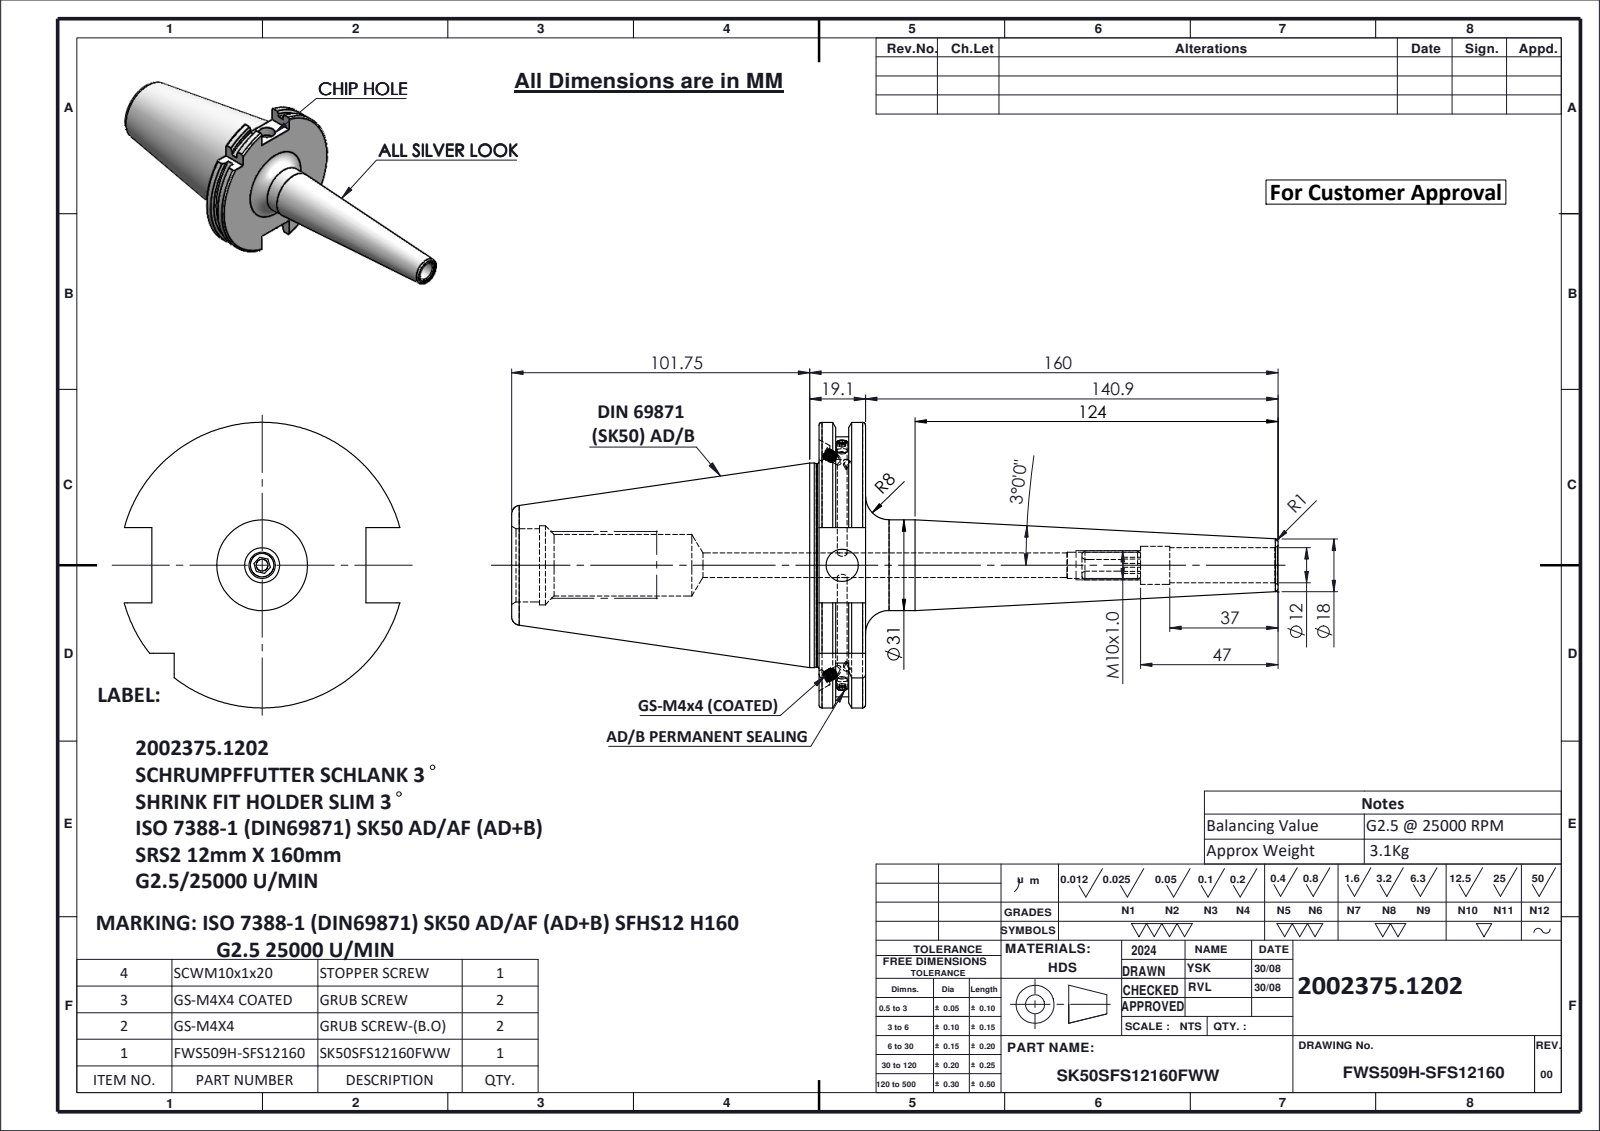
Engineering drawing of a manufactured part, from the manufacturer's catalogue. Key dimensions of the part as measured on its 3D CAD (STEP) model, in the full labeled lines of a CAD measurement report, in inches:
Part name (STEP PRODUCT): SK50SFS12160FWW; FWS509H-SFS12160; GS-M4X4_DIN 913 - M4 x 4-N; SCWM10X1 (+1 more)
STEP written by: SolidWorks 2024 (CONFIG_CONTROL_DESIGN)
Units: inches
Bodies: 6 solids, 275 faces (72 planar, 81 cylindrical, 122 other)
Overall size (bounding box): 10.305 × 3.839 × 3.703
Volume: 24.36 in³ · Surface area: 91.68 in²
Round holes (diameter × count): ⌀0.126 ×2, ⌀0.236 ×2, ⌀0.13 ×1, ⌀0.157 ×1, ⌀0.331 ×1, ⌀0.354 ×1, ⌀0.433 ×1, ⌀0.472 ×1, ⌀0.512 ×1, ⌀0.827 ×1, ⌀0.984 ×1, ⌀1.063 ×1
Round bosses / shafts (diameter × count): ⌀0.157 ×4, ⌀0.114 ×2, ⌀2.75 ×1, ⌀2.734 ×1, ⌀1.22 ×1, ⌀0.394 ×1
Partial cylindrical surfaces — rounded edges, fillets, slot ends (radius × count): R1.768 ×1, R1.919 ×1
Main face-to-face distances: 0.626, 0.223, 0.403, 0.399, 0.176, 0.227, 4.132, 4.355, 4.531, 4.758
